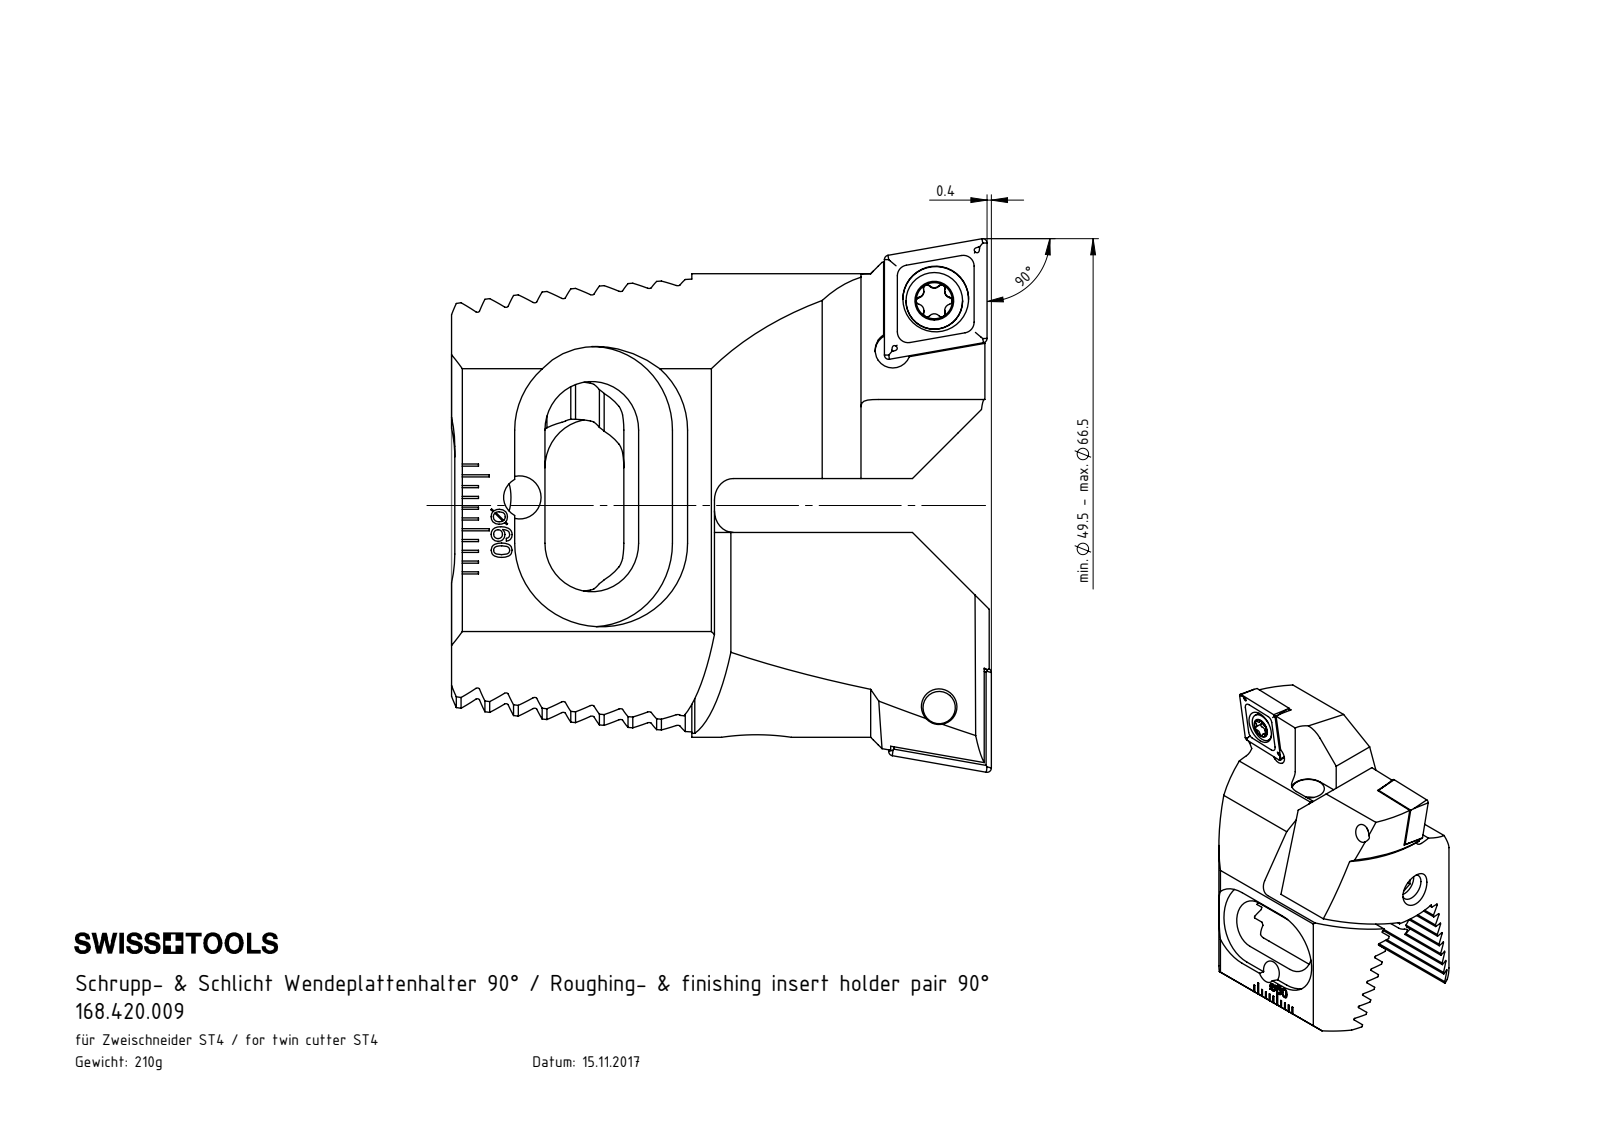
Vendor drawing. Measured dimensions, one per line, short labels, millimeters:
name: Z42-ER3.001.016; CCMT09T304; ISO 4028 - M3 x 5_M3x8; WCB-ER2.001.009_A (+3 more)
written by: SolidWorks 2017 (CONFIG_CONTROL_DESIGN)
unit: mm
bodies: 8 solids, 657 faces (343 planar, 132 cylindrical, 182 other)
size: 50.1 × 49.5 × 34.2
volume: 26 842 mm³; area: 13 156 mm²
holes: 4× ⌀3.3, 2× ⌀4.4, 2× ⌀6.1, 1× ⌀1.6, 1× ⌀2.5, 1× ⌀4, 1× ⌀5, 1× ⌀6
bosses: 3× ⌀4, 2× ⌀5.25, 1× ⌀6, 1× ⌀3, 1× ⌀2
rounds: 16× R0.2, 12× R0.34, 12× R0.59, 4× R2, 4× R4.5, 4× R7.75, 4× R12, 4× R21
face distances: 2.38, 4.76, 11.91, 9.53, 14.29, 7.15, 5.5, 4.77, 7.14, 0.5
hole spacings: 6.19, 33.71, 5.99, 6.07, 12, 28.78, 33.55, 33.81
